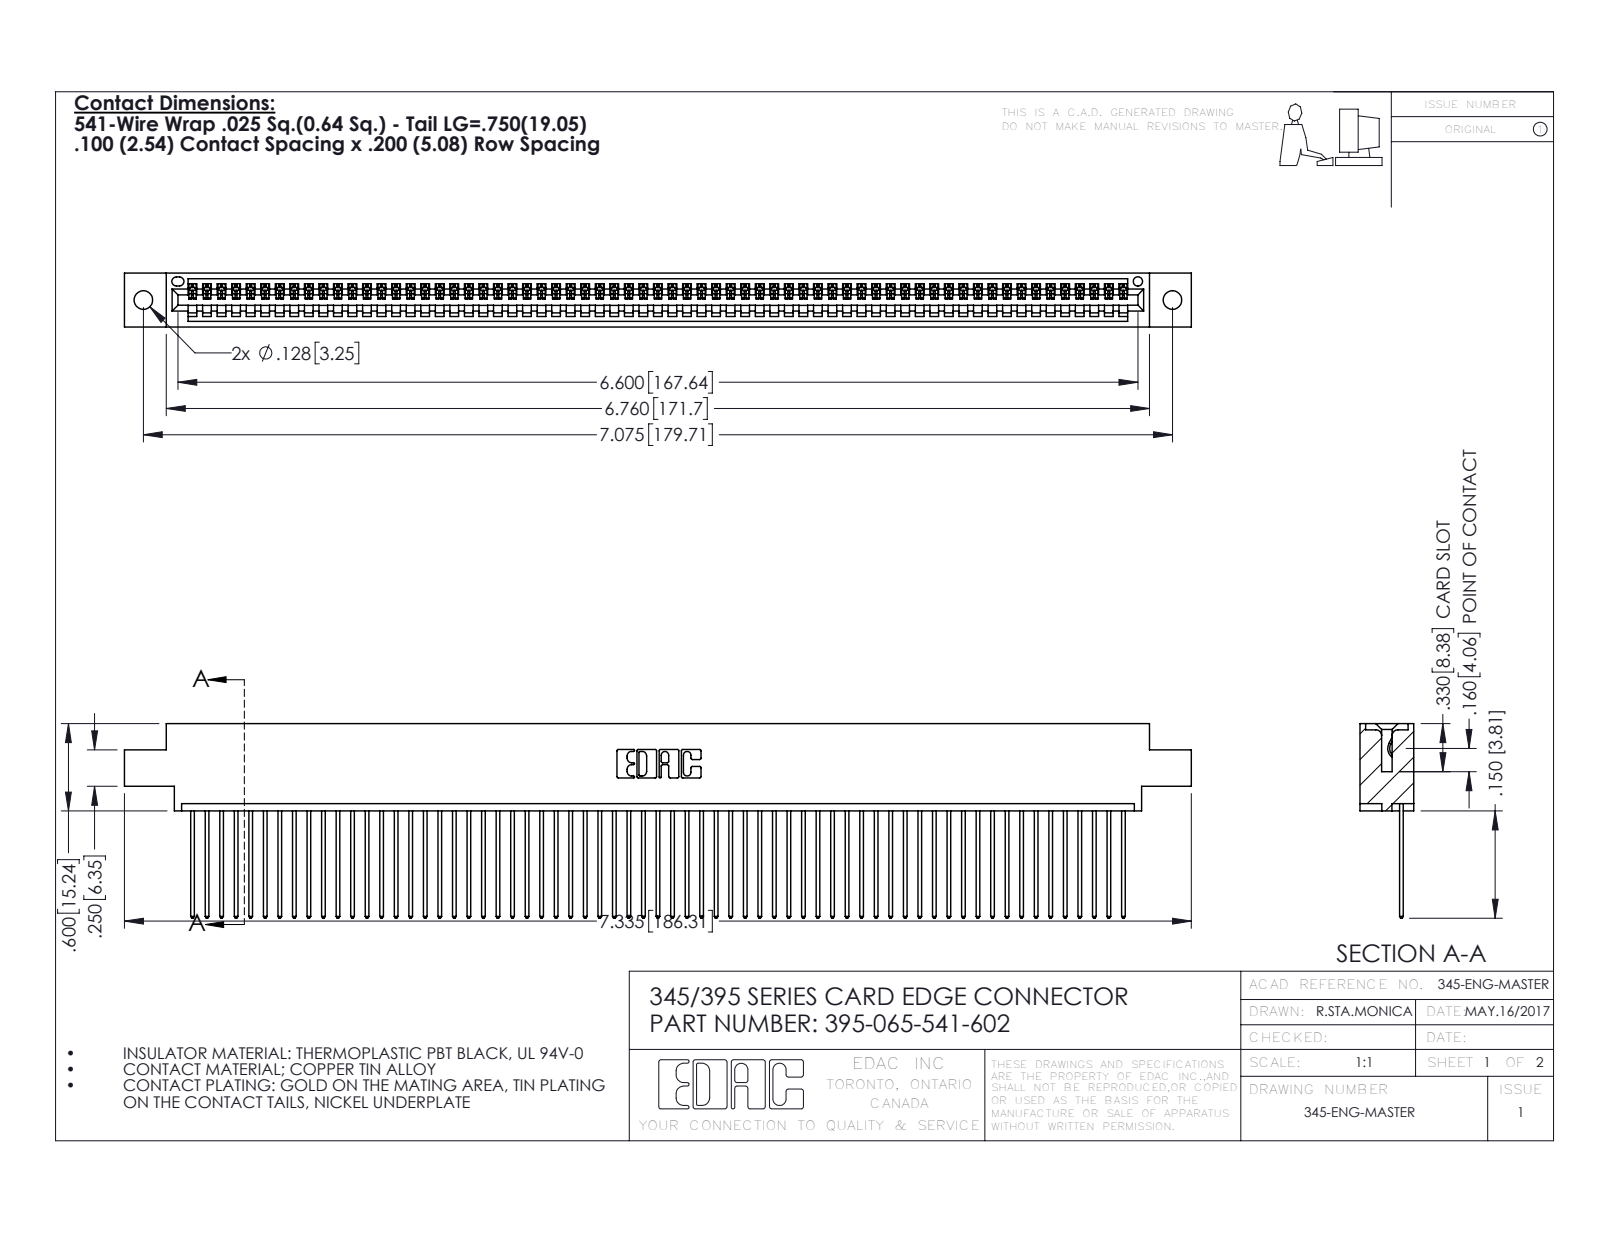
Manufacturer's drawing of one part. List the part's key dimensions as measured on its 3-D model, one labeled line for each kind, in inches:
Part name (STEP PRODUCT): 395-065-541-602; 345 Part_0.170 Offset - 0.128 Dia; 345-292-001_345-293-141
STEP written by: SolidWorks 2016 (CONFIG_CONTROL_DESIGN)
Units: inches
Bodies: 66 solids, 3900 faces (2684 planar, 1216 cylindrical, 0 other)
Overall size (bounding box): 7.335 × 1.337 × 0.37
Volume: 1.095 in³ · Surface area: 39.19 in²
Round holes (diameter × count): ⌀0.128 ×2, ⌀0.064 ×1
Partial cylindrical surfaces — rounded edges, fillets, slot ends (radius × count): R0.006 ×130, R0.01 ×130, R0.01 ×22, R0.007 ×6, R0.031 ×6, R0.026 ×3, R0.031 ×2, R0.04 ×2
Main face-to-face distances: 0.072, 0.298, 0.098, 0.272, 0.025, 0.37, 0.2, 0.225, 0.175, 0.149
Hole centre spacings: 0.27, 6.839, 7.075
